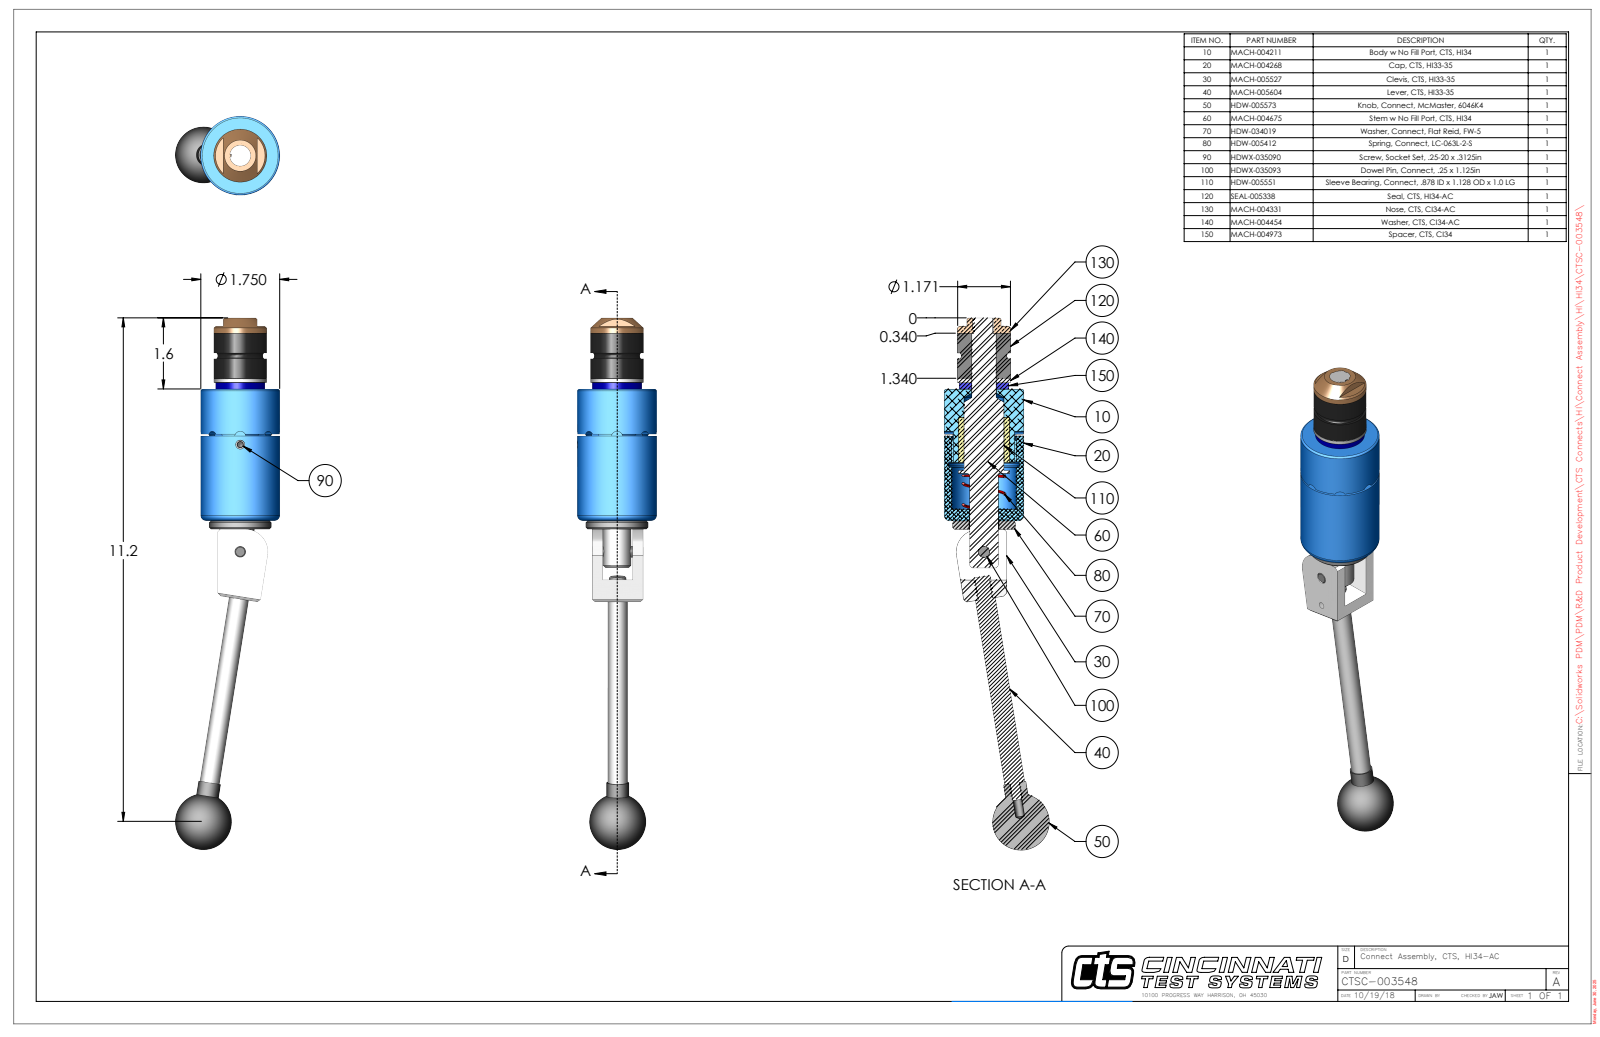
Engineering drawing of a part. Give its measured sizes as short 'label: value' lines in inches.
name: CTSC-003548
written by: SolidWorks 2023 (AUTOMOTIVE_DESIGN)
unit: in
bodies: 10 solids, 254 faces (93 planar, 102 cylindrical, 59 other)
size: 11.792 × 2.312 × 1.75
volume: 11.74 in³; area: 70.06 in²
holes: 2× ⌀0.201, 1× ⌀0.15, 1× ⌀0.249, 1× ⌀0.251, 1× ⌀0.313, 1× ⌀0.422, 1× ⌀0.53, 1× ⌀0.541, 1× ⌀0.547, 1× ⌀0.635, 1× ⌀0.656, 1× ⌀1.419
bosses: 2× ⌀0.5, 2× ⌀0.44, 2× ⌀0.25, 1× ⌀1.75, 1× ⌀1.38, 1× ⌀1.171, 1× ⌀1.09, 1× ⌀0.625
rounds: 4× R0.125, 2× R0.029, 1× R0.5, 1× R0.695, 1× R0.826
face distances: 2.918, 1.237, 1, 4.155, 0.237, 3.155, 1.094, 0.094, 0.143, 3.061
hole spacings: 0.74, 2.376, 3.116
